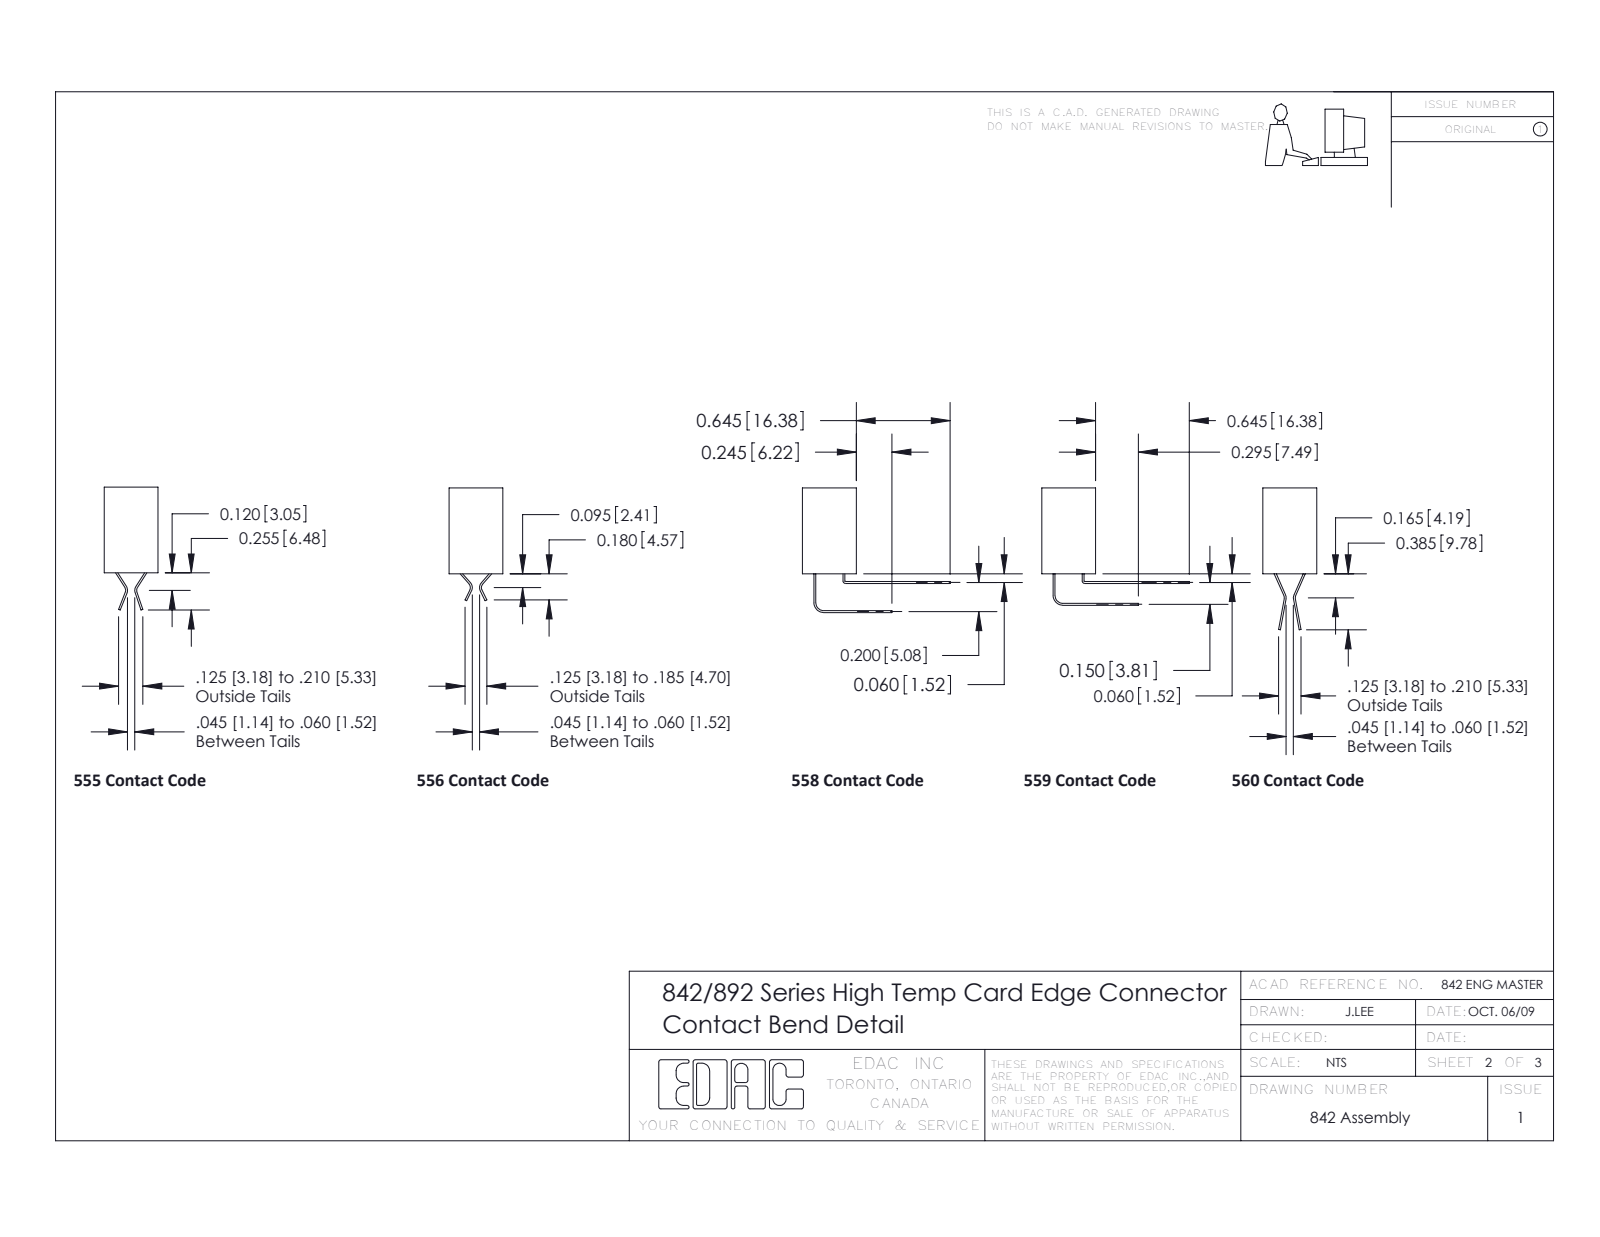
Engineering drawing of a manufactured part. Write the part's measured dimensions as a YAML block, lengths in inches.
part_name: "892-013-500-101; 345-292-001_345-293-100; 842 Part_Lugless"
step_written_by: "SolidWorks 2020 (CONFIG_CONTROL_DESIGN)"
units: inches
bodies: {solids: 14, faces: 804, planar: 530, cylindrical: 274, other: 0}
overall_size: [1.546, 0.86, 0.37]
volume: 0.229
surface_area: 8.244
partial_cylinders:
  - {radius: 0.006, count: 26}
  - {radius: 0.016, count: 26}
  - {radius: 0.02, count: 26}
  - {radius: 0.01, count: 22}
  - {radius: 0.007, count: 6}
  - {radius: 0.031, count: 6}
  - {radius: 0.026, count: 3}
  - {radius: 0.014, count: 1}
face_to_face_distances: [0.2, 0.072, 0.298, 0.1, 0.3, 0.37, 0.4, 0.04, 0.06, 0.16]
